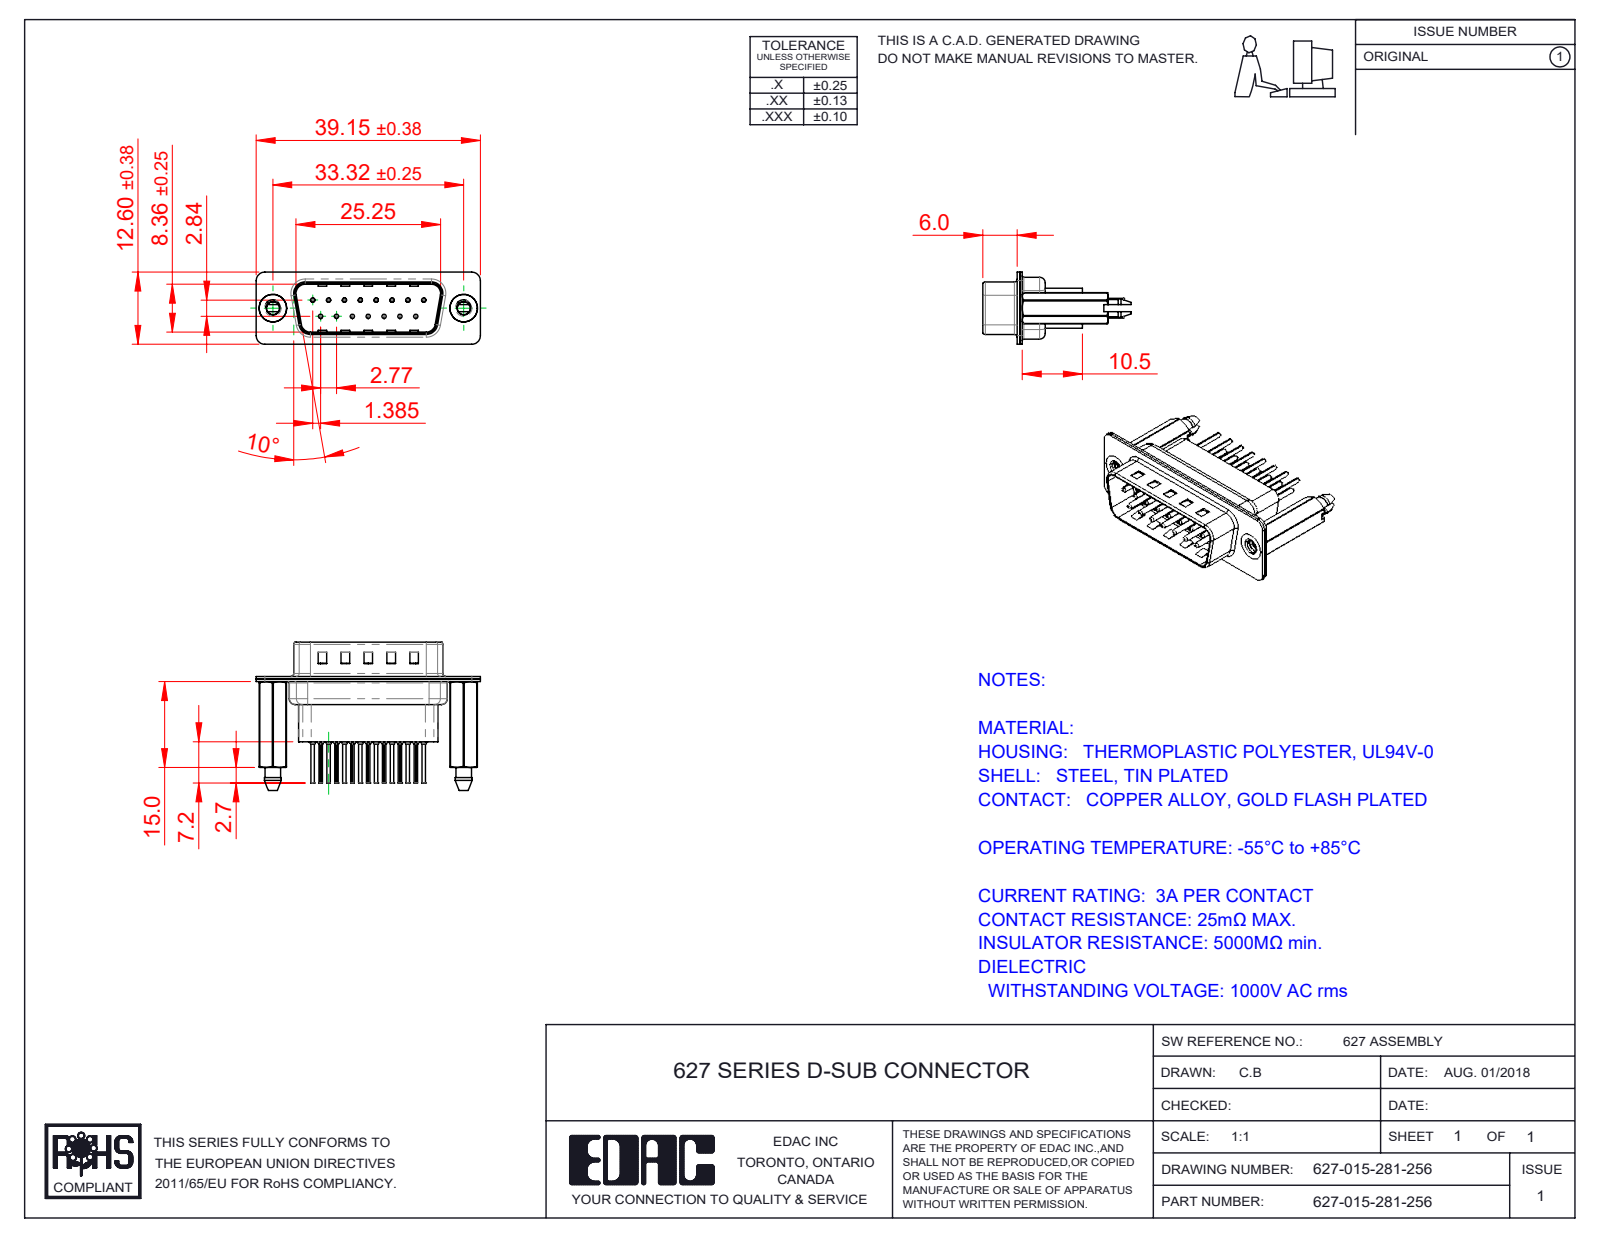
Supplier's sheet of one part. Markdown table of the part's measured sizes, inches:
| quantity | value |
| --- | --- |
| part name | 627 Contact Row 2_61; 627 Contact Row 1_61; 627 Shell Front_15 Contacts; 627 Shell Rear_15 Contacts (+3 more) |
| STEP written by | SolidWorks 2020 (CONFIG_CONTROL_DESIGN) |
| units | inches |
| bodies | 20 solids, 1918 faces (531 planar, 754 cylindrical, 633 other) |
| overall size | 1.541 × 1.02 × 0.496 |
| volume | 0.179 in³ |
| surface area | 11.71 in² |
| round holes (diameter × count) | 0.008 × 15, 0.014 × 15, 0.043 × 15, 0.063 × 15, 0.089 × 2, 0.157 × 2, 0.189 × 2 |
| round bosses / shafts (diameter × count) | 0.079 × 15, 0.059 × 15, 0.03 × 15, 0.024 × 15, 0.193 × 2 |
| partial cylindrical surfaces (radius × count) | 0.004 × 30, 0.059 × 18, 0.079 × 12, 0.063 × 10, 0.02 × 8, 0.01 × 4, 0.024 × 4, 0.026 × 4 |
| main face-to-face distances | 0.016, 0.018, 0.035, 0.032, 0.377, 0.187, 0.059, 0.027, 0.302, 0.055 |
| hole center spacings | 0.124, 0.109, 0.218, 0.327, 0.436, 0.198, 0.198, 0.294 |
